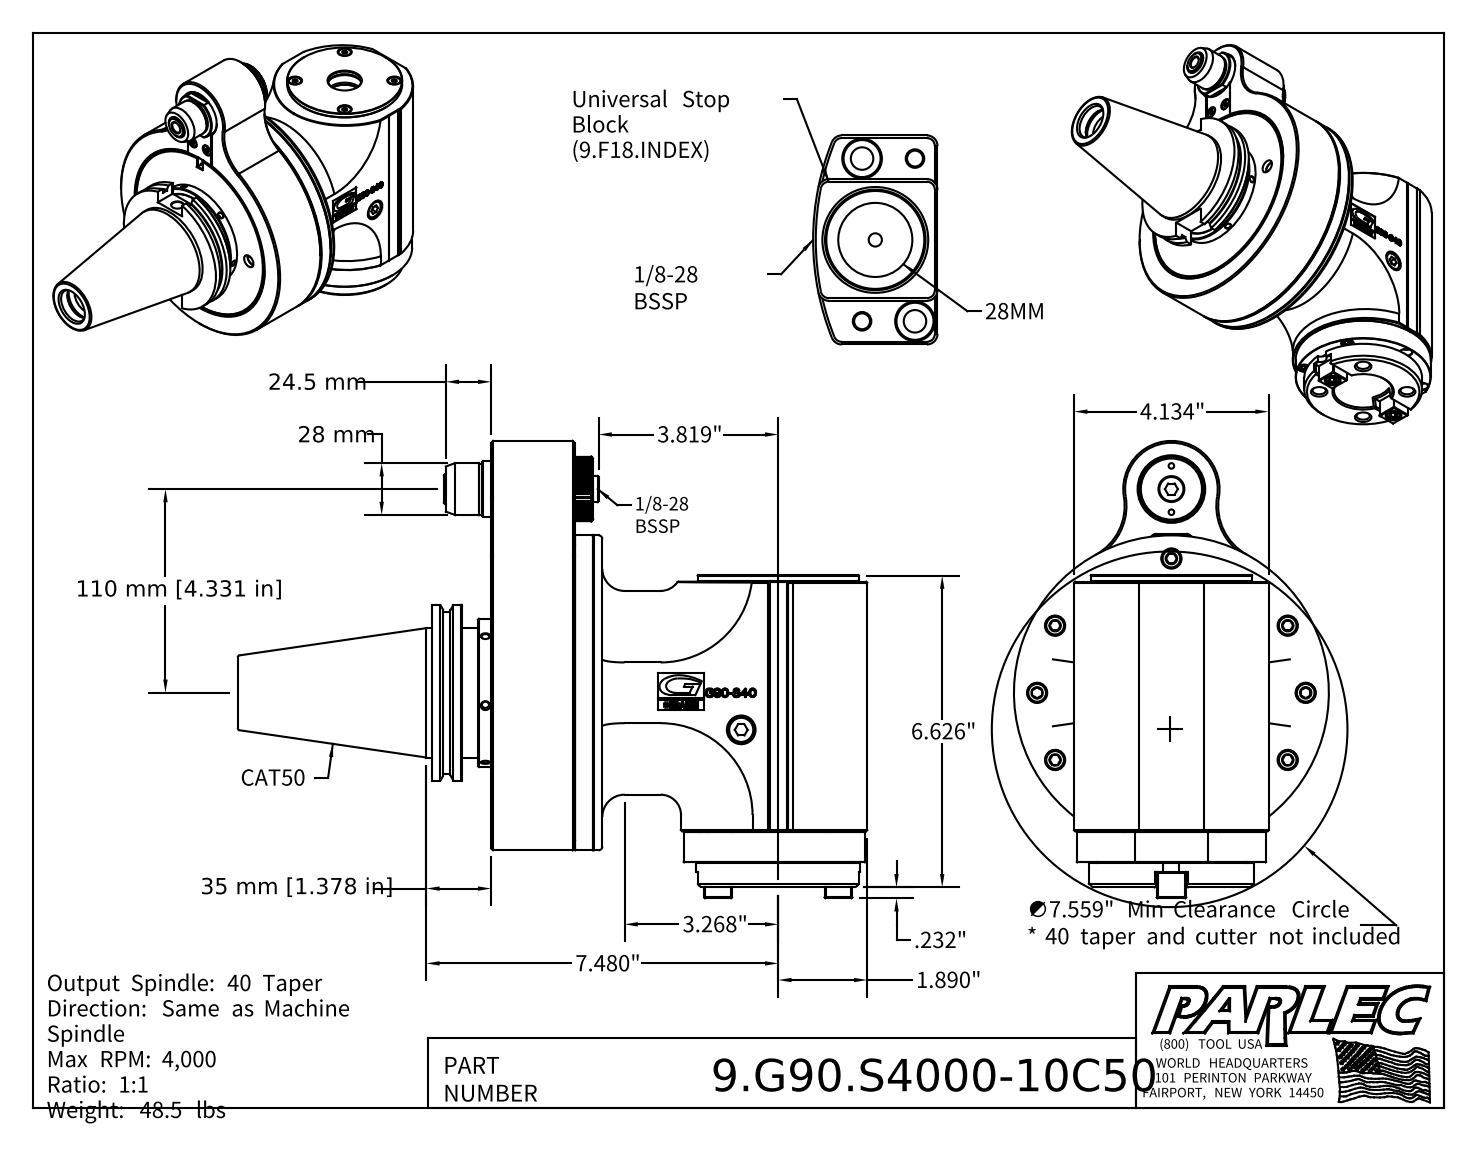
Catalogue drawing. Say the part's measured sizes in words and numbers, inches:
The part is named "9.G90.S4000-10C50". Its 3-D file was written by "Autodesk Inventor 2022 (AUTOMOTIVE_DESIGN)". It is 3 solids with 1854 faces: 1003 planar, 392 cylindrical and 459 other. Overall it measures 13.378 by 9.72 by 6.693 inches. Its volume is 166.1 cubic inches and its surface area 715.2 square inches. Round holes: 20 of diameter 0.165, 13 of diameter 0.256, 11 of diameter 0.197, 11 of diameter 0.413, 6 of diameter 0.217, 6 of diameter 0.354, 6 of diameter 0.394, 5 of diameter 0.335, 4 of diameter 0.098, 2 of diameter 0.118, 2 of diameter 0.205, 2 of diameter 0.362. Round bosses or shafts: 9 of diameter 0.394, 7 of diameter 0.236, 4 of diameter 0.386, 3 of diameter 1.378, 2 of diameter 0.551, 2 of diameter 0.504, 2 of diameter 0.354, 2 of diameter 0.335. Partial cylindrical surfaces (rounded edges, fillets, slot ends): 18 of radius 0.118, 16 of radius 0.157, 2 of radius 0.177, 2 of radius 0.197, 2 of radius 0.472, 2 of radius 1.181, 1 of radius 0.1, 1 of radius 0.102. The main face-to-face distances are 0.591, 1.181, 1.772, 0.669, 0.154, 1.618, 2.362, 2.209, 0.63, 0.626. The hole center spacings are 2.854, 1.478, 1.811, 4.037, 4.944, 5.514, 0.849, 1.232.
